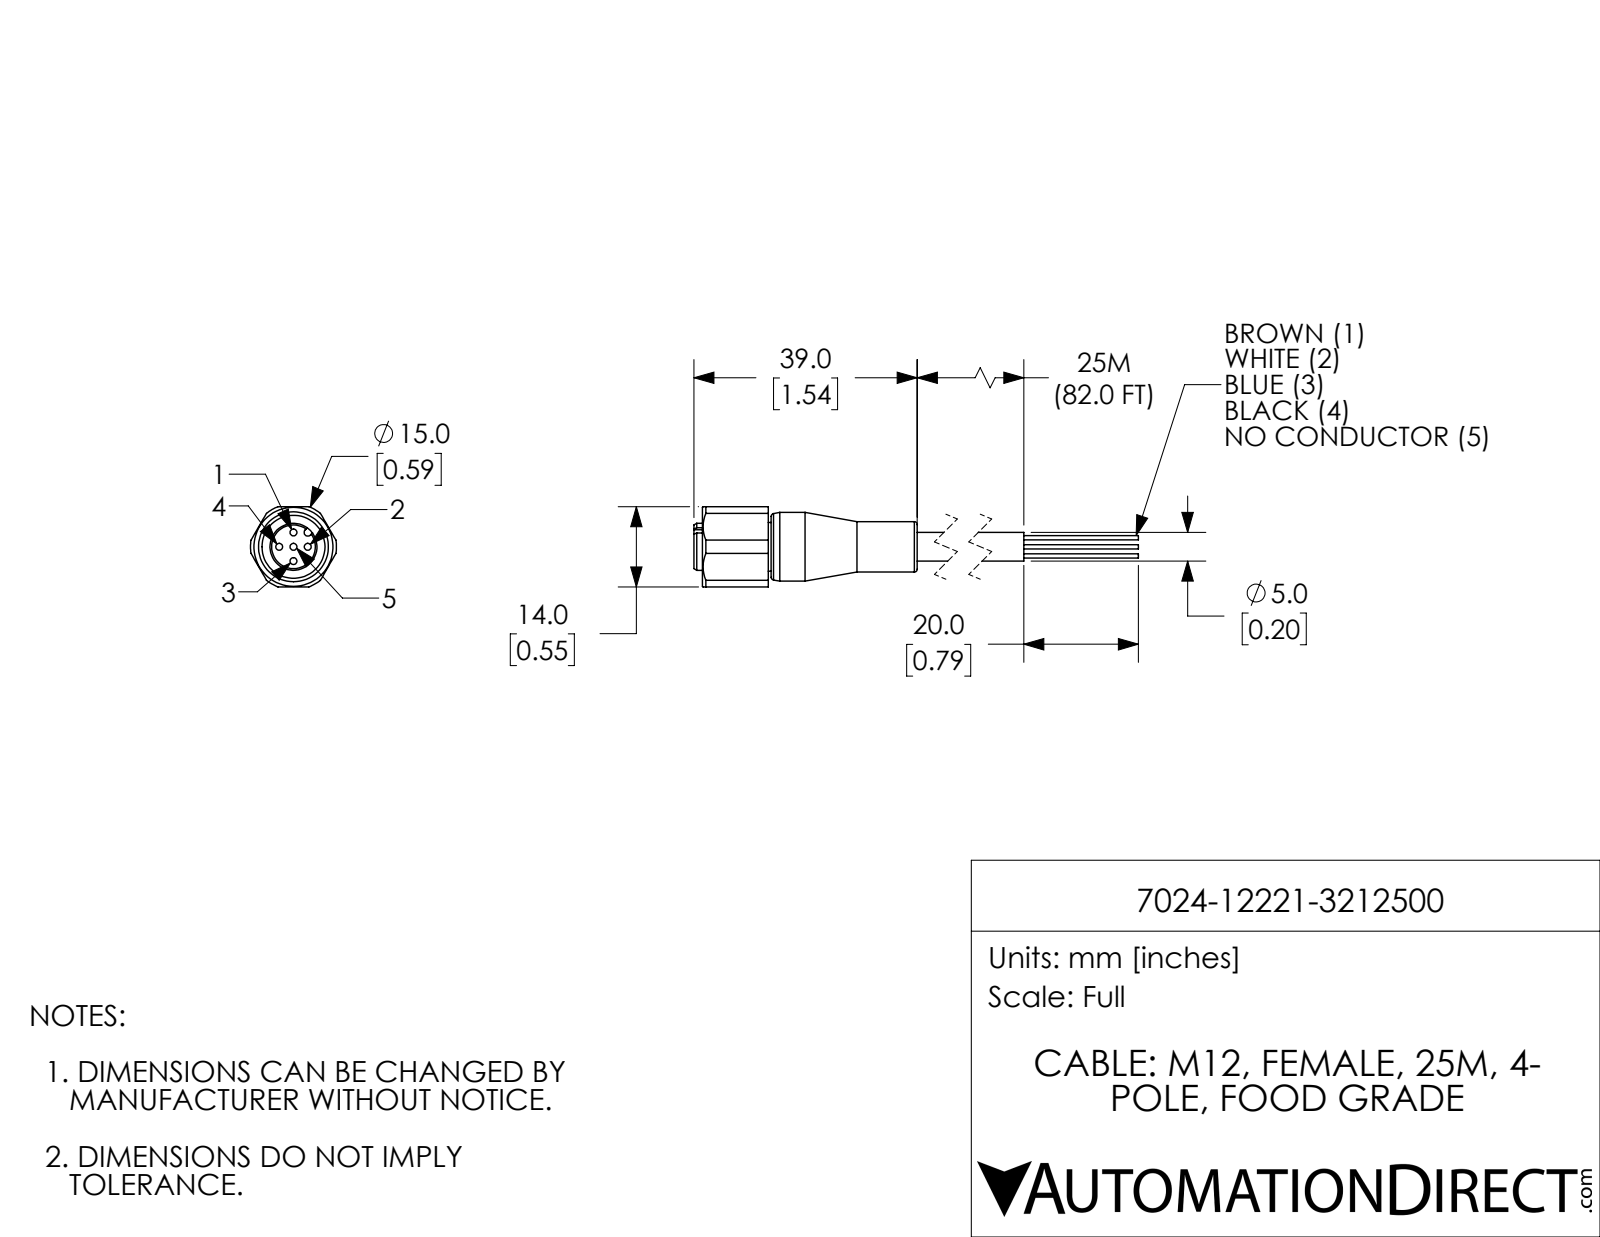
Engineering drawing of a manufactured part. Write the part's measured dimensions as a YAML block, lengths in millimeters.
part_name: "7024-12221-3212500"
step_written_by: "SolidWorks 2018 (AUTOMOTIVE_DESIGN)"
units: millimeters
bodies: {solids: 1, faces: 77, planar: 25, cylindrical: 37, other: 15}
overall_size: [77.8, 15, 14]
volume: 4116
surface_area: 2828
round_holes:
  - {diameter: 1.2, count: 5}
  - {diameter: 11, count: 1}
round_bosses_or_shafts:
  - {diameter: 0.76, count: 4}
  - {diameter: 12, count: 1}
  - {diameter: 8.8, count: 1}
  - {diameter: 8.5, count: 1}
  - {diameter: 8.2, count: 1}
  - {diameter: 5, count: 1}
partial_cylinders:
  - {radius: 0.65, count: 1}
  - {radius: 7.5, count: 1}
face_to_face_distances: [14, 4, 9, 13, 1.5, 7.5, 11.5, 13.5, 12, 4.5]
hole_center_spacings: [2.5, 3.54, 5]
